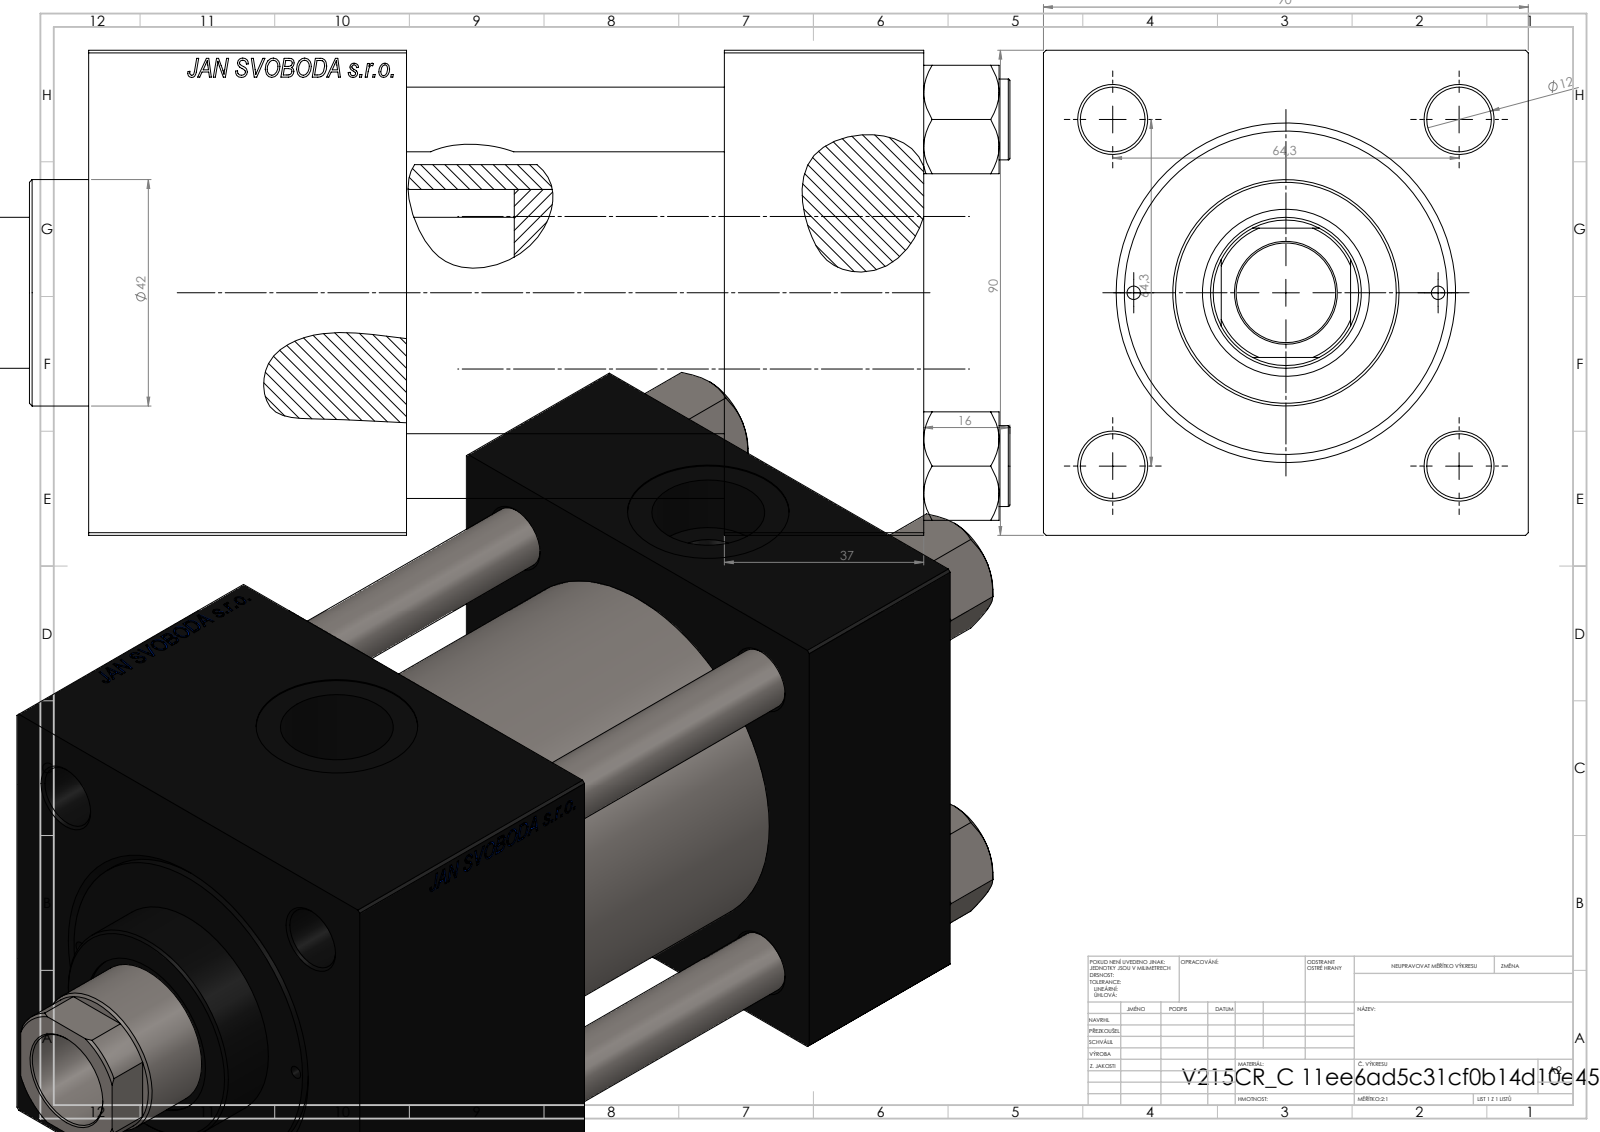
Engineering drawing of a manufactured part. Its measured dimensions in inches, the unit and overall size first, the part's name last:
Units: inches
Overall size (bounding box): 7.992 × 3.543 × 3.543
Round holes (diameter × count): ⌀0.472 ×4, ⌀0.098 ×2, ⌀0.276 ×2, ⌀0.825 ×2, ⌀1.181 ×2, ⌀0.728 ×1, ⌀1.102 ×1, ⌀1.22 ×1, ⌀1.969 ×1, ⌀2.362 ×1, ⌀2.48 ×1
Round bosses / shafts (diameter × count): ⌀0.591 ×4, ⌀2.717 ×1, ⌀1.654 ×1
Partial cylindrical surfaces — rounded edges, fillets, slot ends (radius × count): R0.531 ×1
Main face-to-face distances: 3.543, 2.323, 1.457, 6.102, 4.646, 3.78, 4.972, 3.516, 1.193, 1.13
Hole centre spacings: 1.275, 1.79, 2.531, 2.694, 1.112, 3.58, 2.224, 3.839
Volume: 57.77 in³ · Surface area: 277.8 in²
Bodies: 11 solids, 1155 faces (528 planar, 91 cylindrical, 536 other)
Part name (STEP PRODUCT): V215CR_C_TYCINKA; NUT_M5_C; V215_VC_A; V215CR_C_Body (+1 more)
STEP written by: SolidWorks 2019 (CONFIG_CONTROL_DESIGN)
